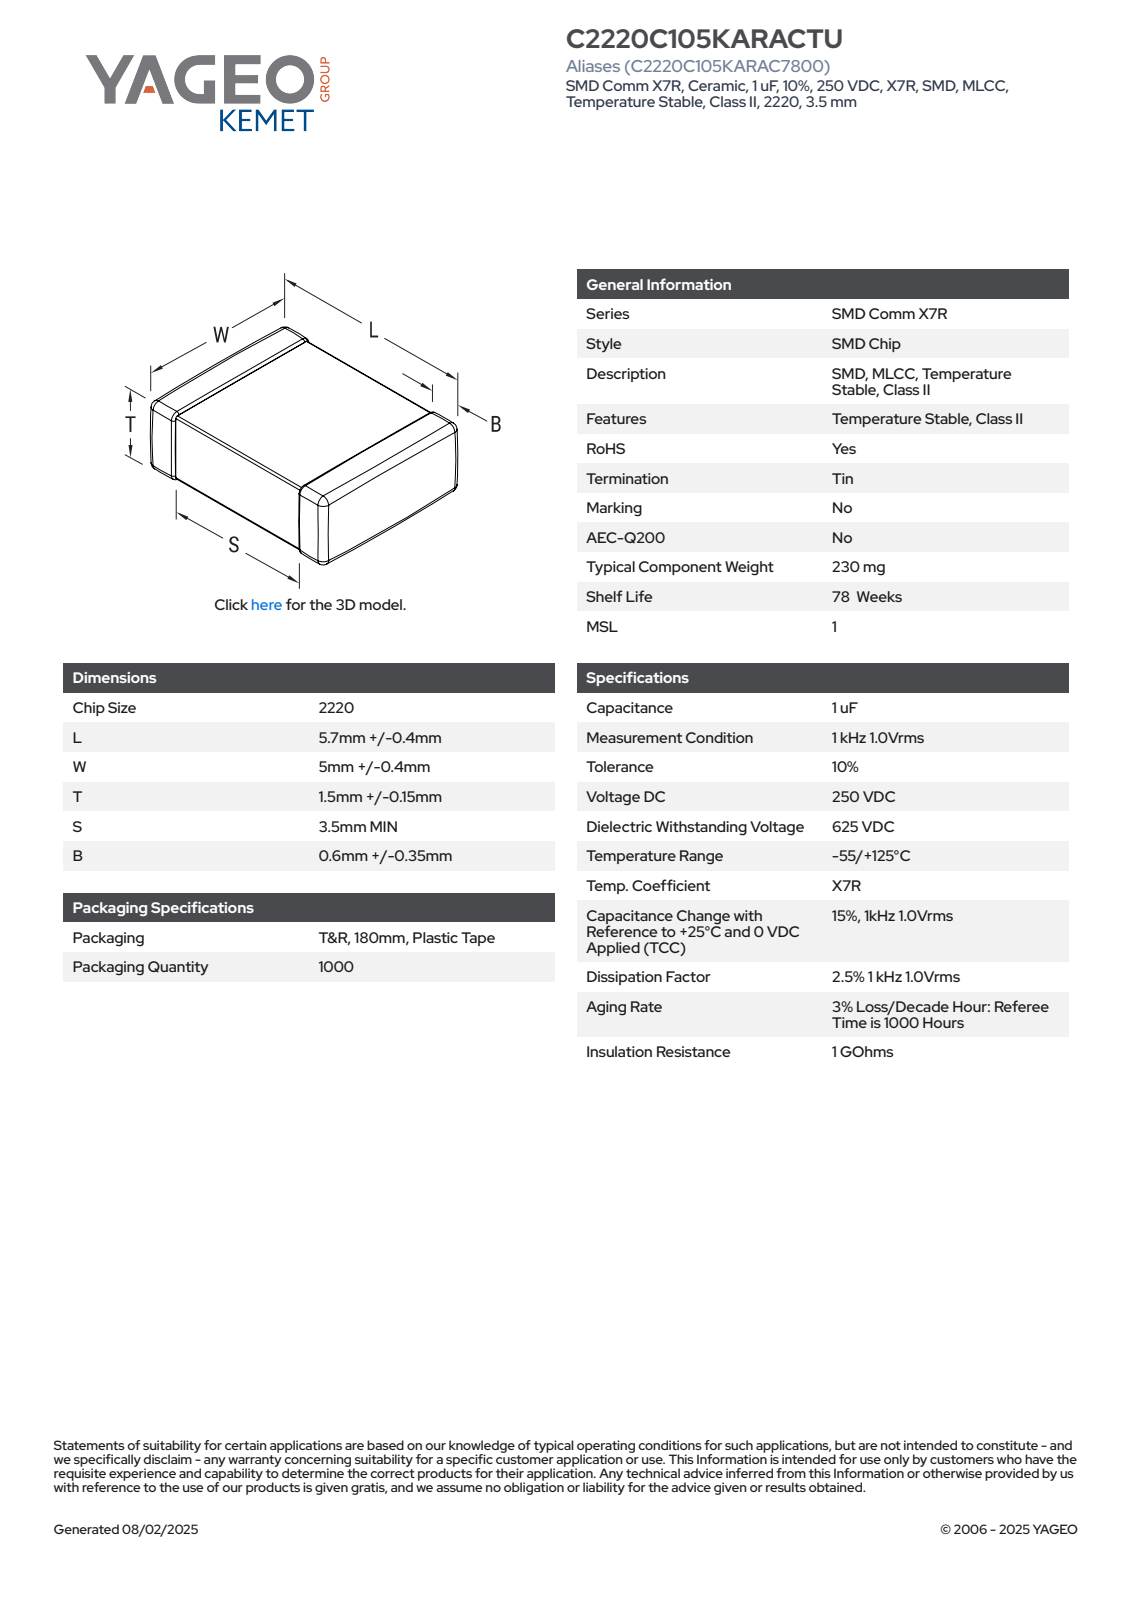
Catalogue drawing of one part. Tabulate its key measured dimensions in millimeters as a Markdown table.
| quantity | value |
| --- | --- |
| part name | CCS_CCSTDNOS_2220_L6.1W5.4T1.65B0.95 |
| STEP written by | SolidWorks 2014 (AUTOMOTIVE_DESIGN) |
| units | millimeters |
| bodies | 4 solids, 125 faces (71 planar, 38 cylindrical, 16 other) |
| overall size | 6.1 × 5.4 × 1.65 |
| volume | 48 mm³ |
| surface area | 100 mm² |
| partial cylindrical surfaces (radius × count) | 0.11 × 24 |
| main face-to-face distances | 1.43, 1.54, 1.65, 6.1, 5.18, 5.29, 5.4, 2.66, 2.74, 2.55 |
